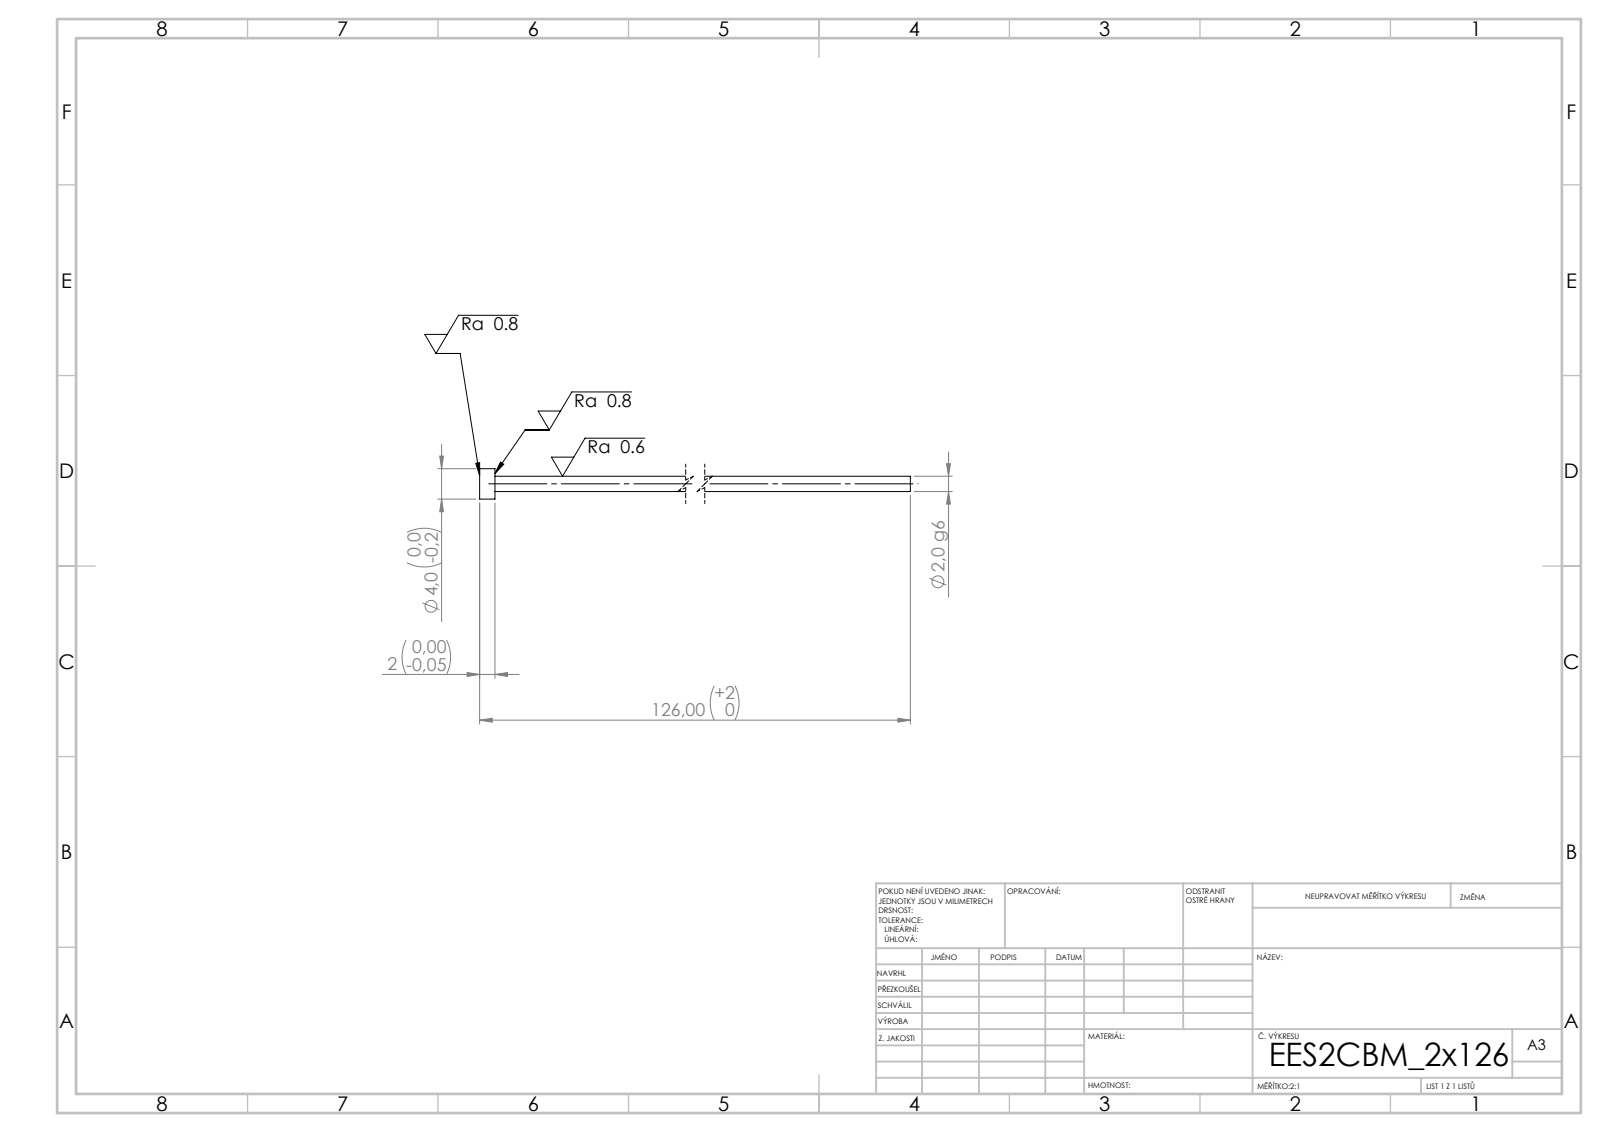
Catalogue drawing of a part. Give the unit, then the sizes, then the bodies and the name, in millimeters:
Units: millimetres
Overall size (bounding box): 126 × 4 × 4
Round bosses / shafts (diameter × count): ⌀4 ×1, ⌀2 ×1
Main face-to-face distances: 2, 126, 124
Volume: 415 mm³ · Surface area: 829 mm²
Bodies: 1 solid, 7 faces (3 planar, 4 cylindrical, 0 other)
STEP written by: SolidWorks 2019 (CONFIG_CONTROL_DESIGN)
